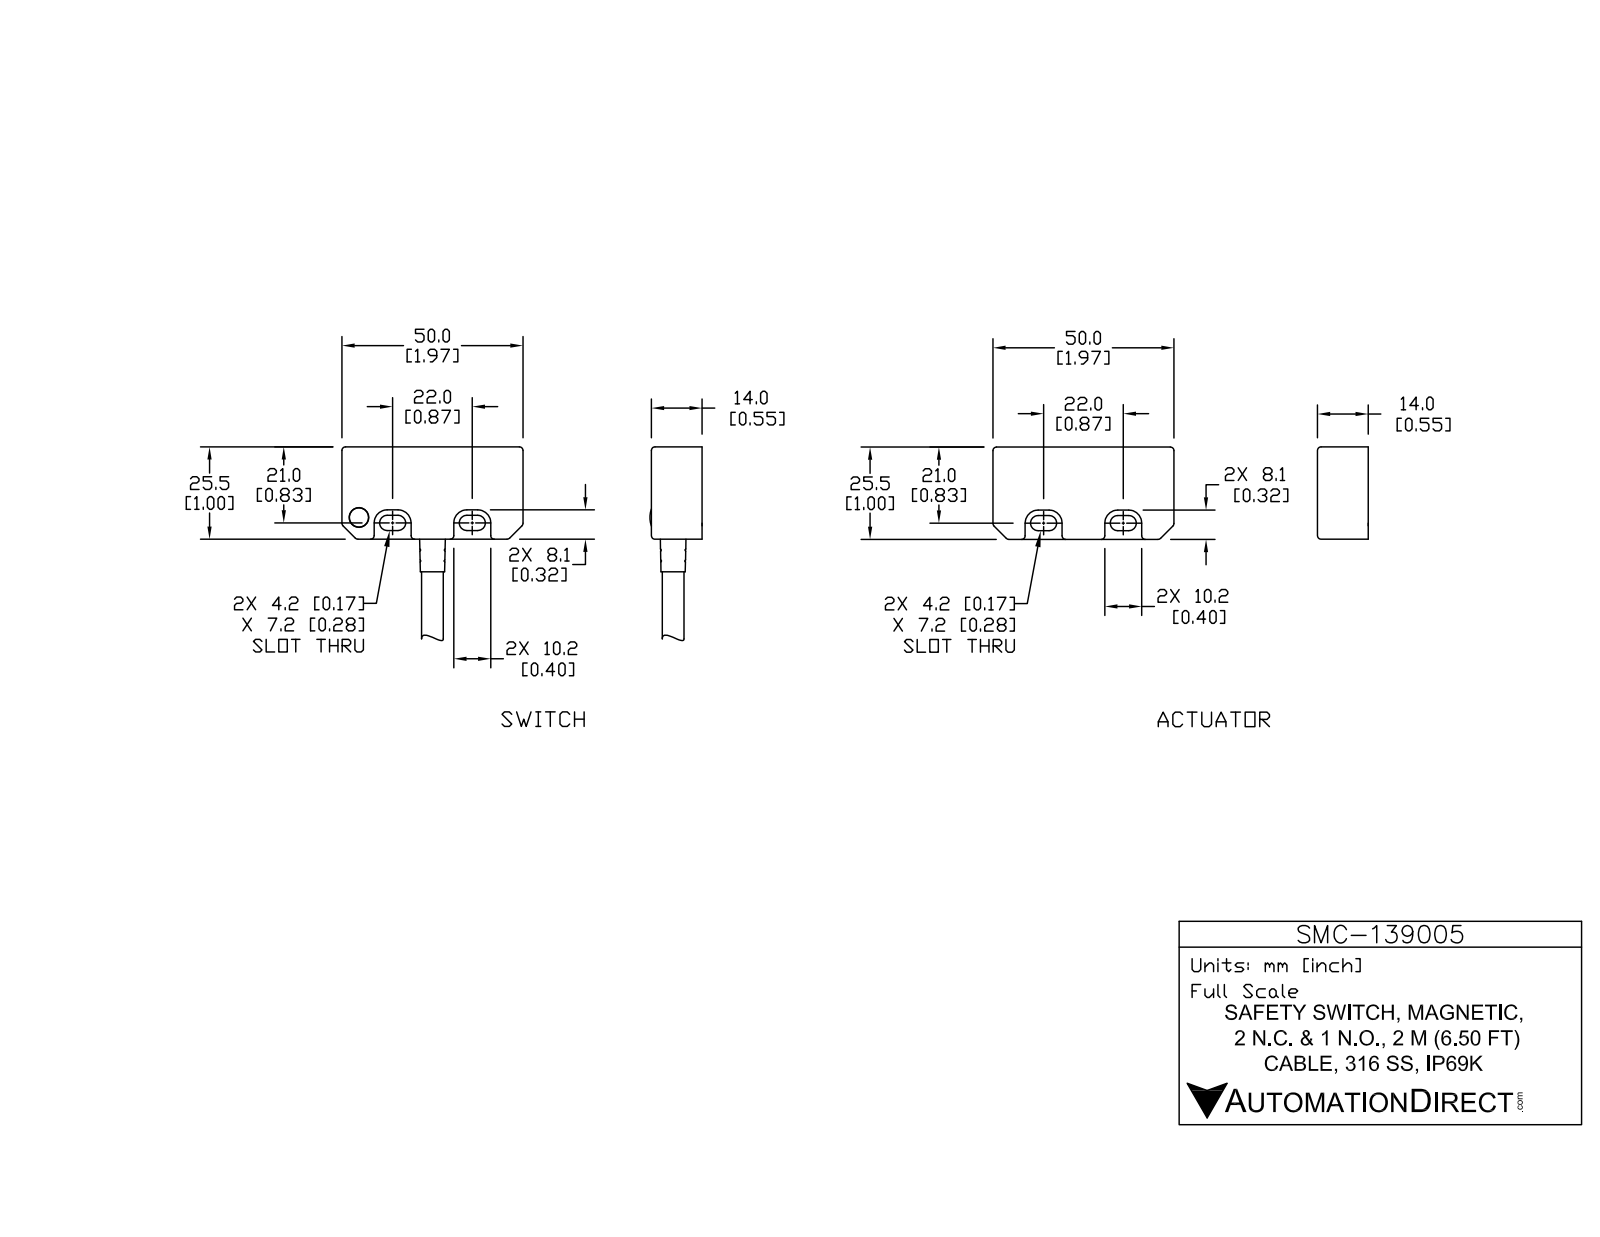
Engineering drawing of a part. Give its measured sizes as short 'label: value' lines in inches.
name: SMC-139005_1; SMC-139005; SMC-139005_2
written by: SolidWorks 2017 (AUTOMOTIVE_DESIGN)
unit: in
bodies: 12 solids, 886 faces (254 planar, 373 cylindrical, 259 other)
size: 8.091 × 1.969 × 0.566
volume: 1.16 in³; area: 36.28 in²
holes: 4× ⌀0.197, 1× ⌀0.119, 1× ⌀0.177, 1× ⌀0.213, 1× ⌀0.232, 1× ⌀0.287
bosses: 4× ⌀0.193, 4× ⌀0.079, 2× ⌀0.031, 1× ⌀0.339, 1× ⌀0.299, 1× ⌀0.28, 1× ⌀0.236, 1× ⌀0.209
rounds: 80× R0.02, 74× R0.012, 40× R0.039, 8× R0.083, 8× R0.122, 8× R0.128, 8× R0.142, 8× R0.175
face distances: 0.059, 0.543, 0.055, 0.488, 0.484, 0.429, 0.098, 0.945, 1.043, 1.909
hole spacings: 0.866, 0.988, 0.472, 1.27, 1.309, 1.319, 1.332, 1.775
